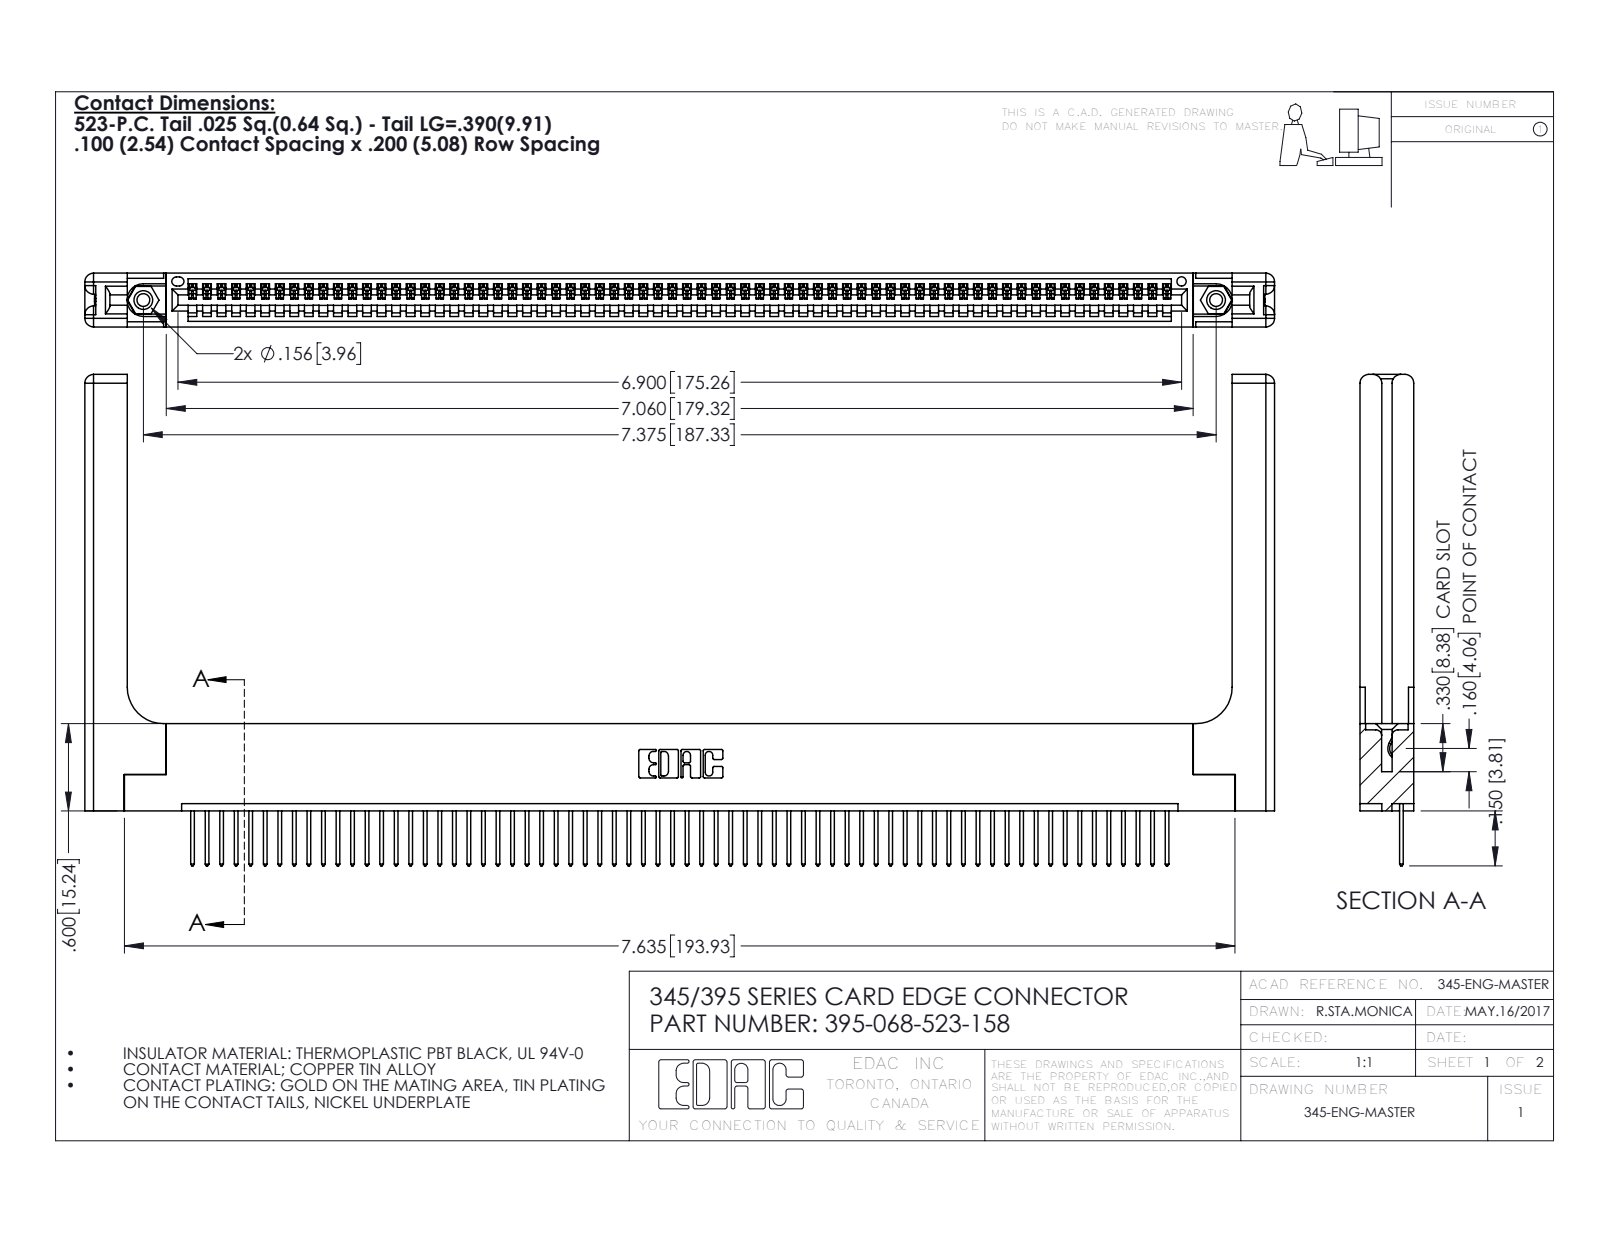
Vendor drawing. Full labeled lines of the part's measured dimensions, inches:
Part name (STEP PRODUCT): 345 Part_Flush Mounting Lugs - 0.156 Dia-TH; 395-068-523-158; 345-220-058_345-220-058; 345-292-001_345-293-123 (+1 more)
STEP written by: SolidWorks 2016 (CONFIG_CONTROL_DESIGN)
Units: inches
Bodies: 73 solids, 4326 faces (2948 planar, 1318 cylindrical, 60 other)
Overall size (bounding box): 8.179 × 3.377 × 0.37
Volume: 1.735 in³ · Surface area: 49.91 in²
Round holes (diameter × count): ⌀0.089 ×2, ⌀0.125 ×2, ⌀0.156 ×2, ⌀0.064 ×1
Round bosses / shafts (diameter × count): ⌀0.155 ×2
Partial cylindrical surfaces — rounded edges, fillets, slot ends (radius × count): R0.006 ×136, R0.01 ×136, R0.01 ×22, R0.06 ×16, R0.007 ×6, R0.031 ×6, R0.026 ×3, R0.03 ×2
Main face-to-face distances: 0.072, 0.298, 0.37, 0.2, 0.098, 0.272, 0.025, 0.225, 0.148, 0.15
Hole centre spacings: 0.27, 7.139, 7.375
